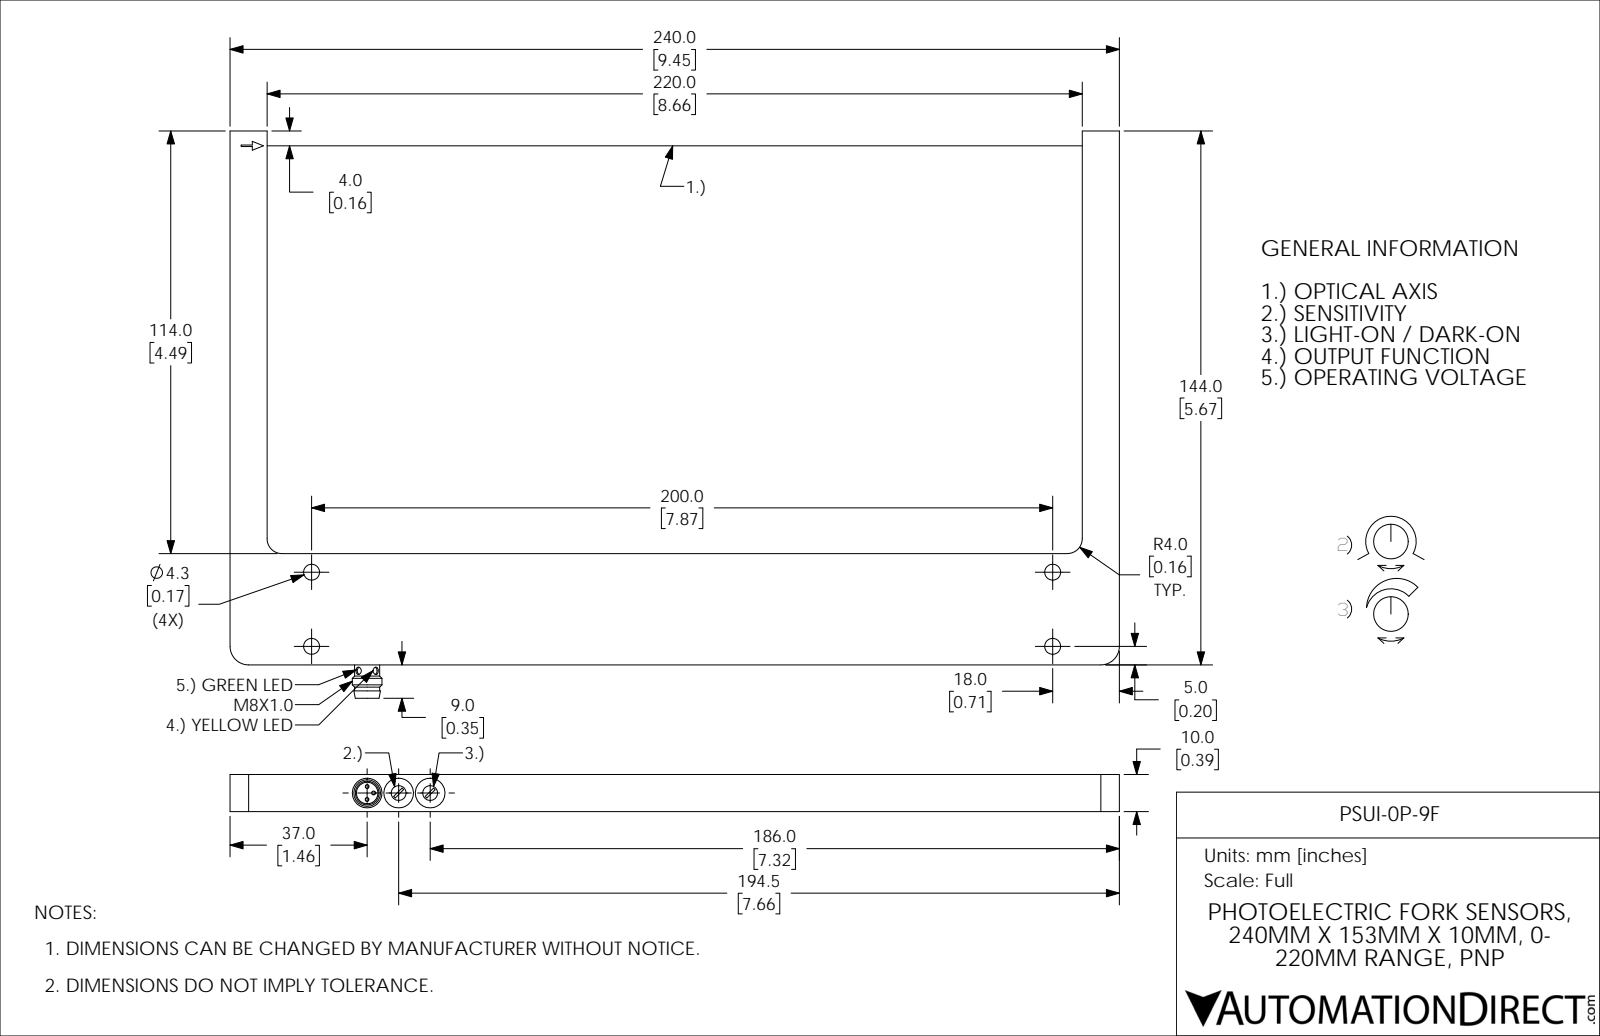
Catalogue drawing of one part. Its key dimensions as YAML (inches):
part_name: "PSUI-0P-9F"
step_written_by: "SolidWorks 2017 (AUTOMOTIVE_DESIGN)"
units: inches
bodies: {solids: 1, faces: 68, planar: 35, cylindrical: 27, other: 6}
overall_size: [9.449, 6.024, 0.394]
volume: 5.76
surface_area: 45.93
round_holes:
  - {diameter: 0.169, count: 4}
  - {diameter: 0.079, count: 2}
  - {diameter: 0.157, count: 2}
  - {diameter: 0.315, count: 2}
  - {diameter: 0.228, count: 1}
round_bosses_or_shafts:
  - {diameter: 0.039, count: 3}
  - {diameter: 0.315, count: 1}
  - {diameter: 0.267, count: 1}
partial_cylinders:
  - {radius: 0.063, count: 2}
  - {radius: 0.157, count: 2}
  - {radius: 0.197, count: 2}
face_to_face_distances: [0.394, 9.055, 1.181, 9.449, 8.661, 4.488, 5.669, 5.665, 1.177, 0.157]
hole_center_spacings: [0.335, 0.787, 7.874, 7.913, 0.669]
